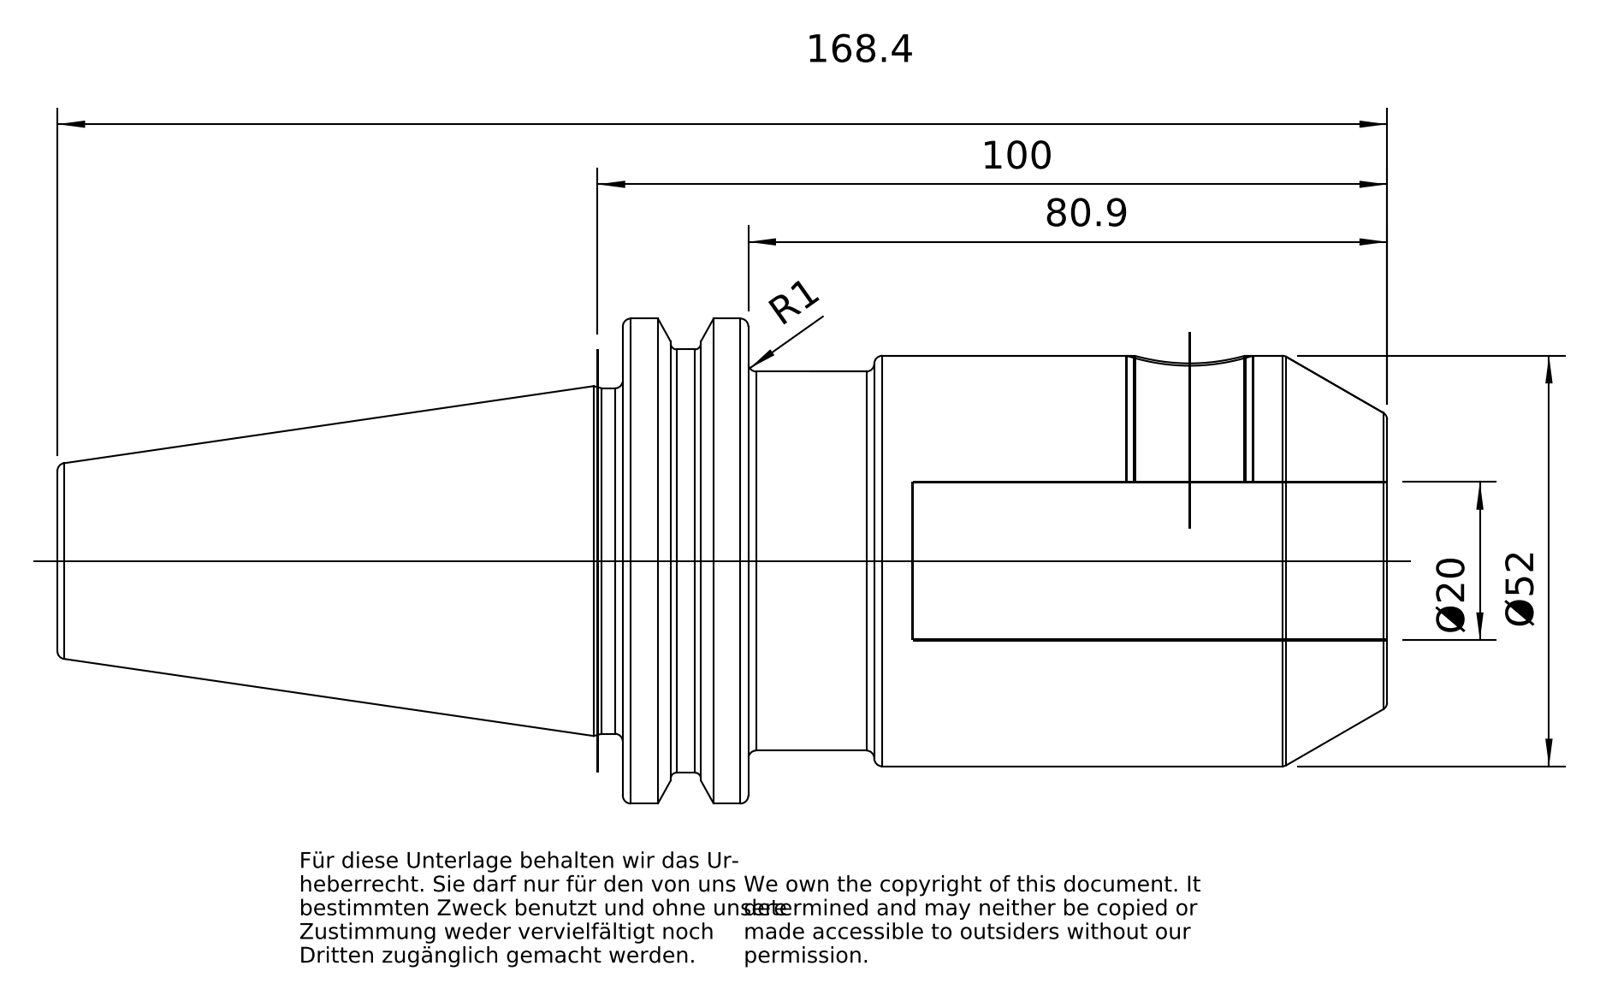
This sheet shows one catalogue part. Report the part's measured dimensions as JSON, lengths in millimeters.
{"part_name": "40-301-20", "step_written_by": "PRO/ENGINEER BY PARAMETRIC TECHNOLOGY CORPORATION, 2010430 (CONFIG_CONTROL_DESIGN)", "units": "millimeters", "bodies": {"solids": 1, "faces": 106, "planar": 23, "cylindrical": 30, "other": 53}, "overall_size": [168.25, 63.52, 61.42], "volume_mm3": 244022, "surface_area_mm2": 37434, "round_holes": [[13.84, 1], [14, 1], [16, 1], [17.01, 1], [17.5, 1], [20, 1]], "round_bosses_or_shafts": [[52, 1], [48, 1], [43.75, 1], [16.01, 1]], "partial_cylinders_radius": [[1.35, 1], [28, 1], [31.76, 1]], "face_to_face_distances": [15.85, 96.8, 80.95, 36.7, 20.85, 60.1, 47.4, 16.2, 71.45, 87.3]}
